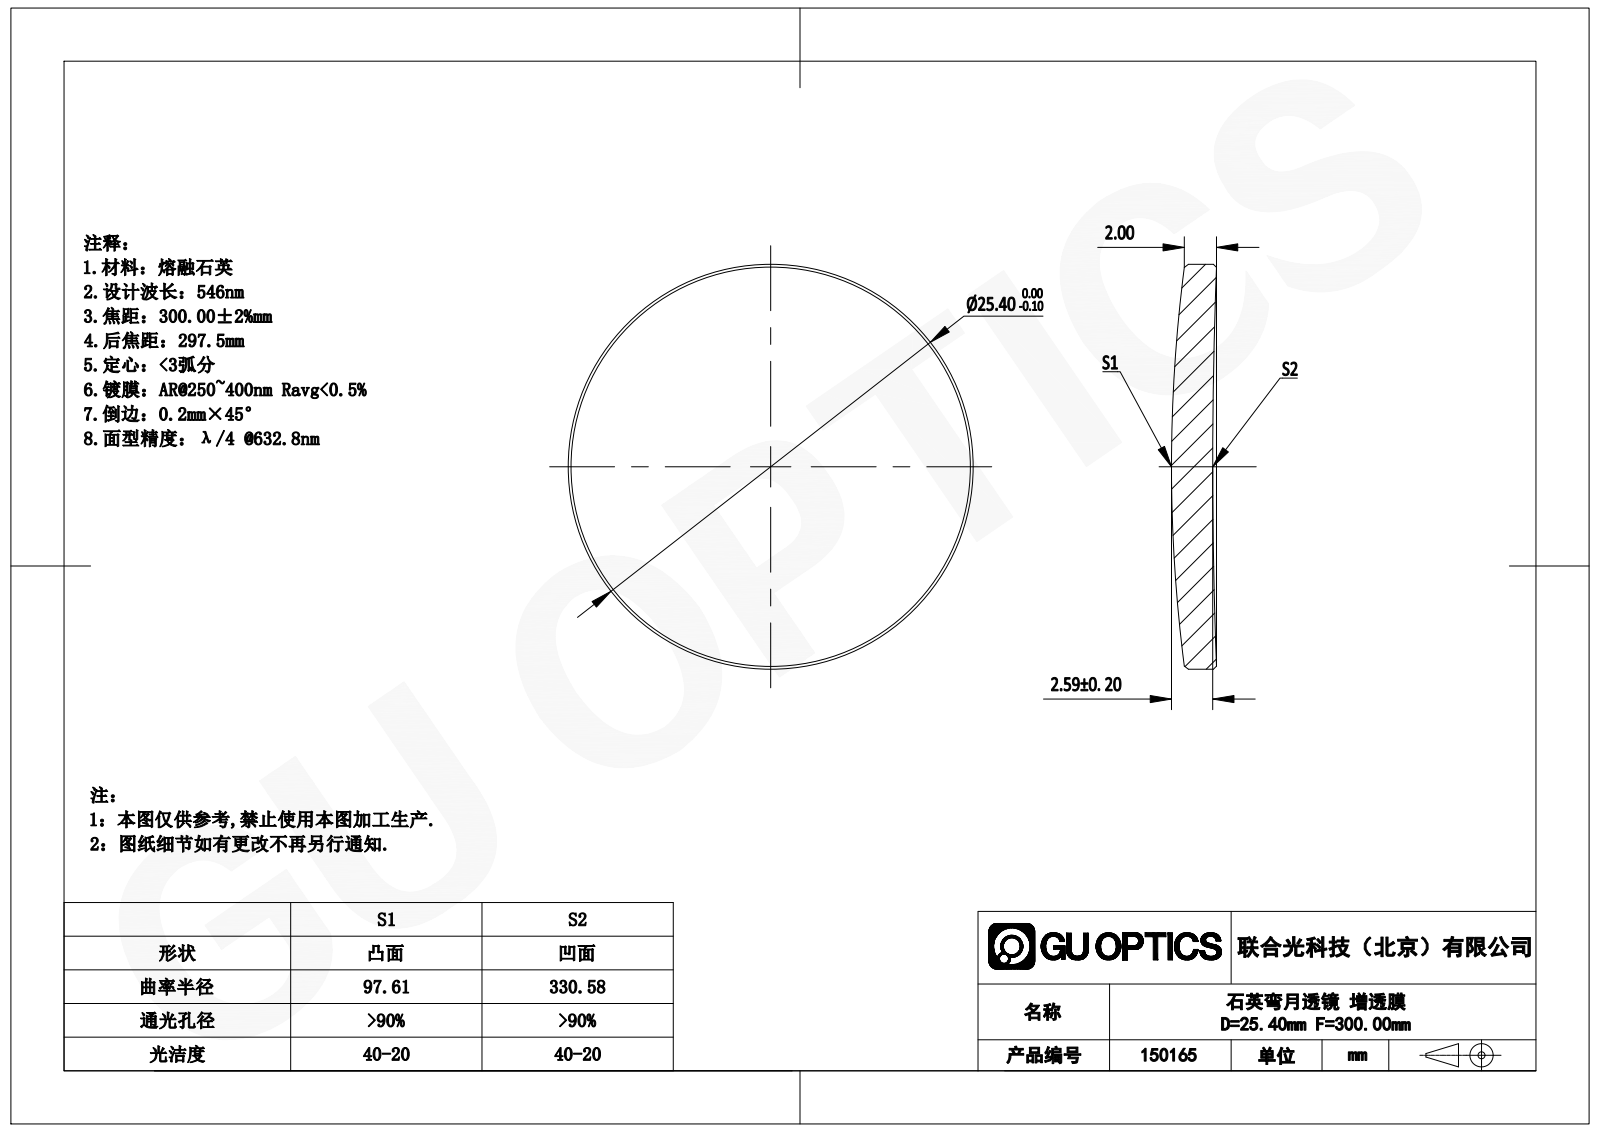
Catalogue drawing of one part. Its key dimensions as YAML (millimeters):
part_name: "GLM2-025B-300-UV"
step_written_by: "SolidWorks 2022 (AUTOMOTIVE_DESIGN)"
units: millimeters
bodies: {solids: 1, faces: 10, planar: 0, cylindrical: 2, other: 8}
overall_size: [25.4, 25.4, 2.82]
volume: 1159
surface_area: 1157
round_bosses_or_shafts:
  - {diameter: 25.4, count: 1}
